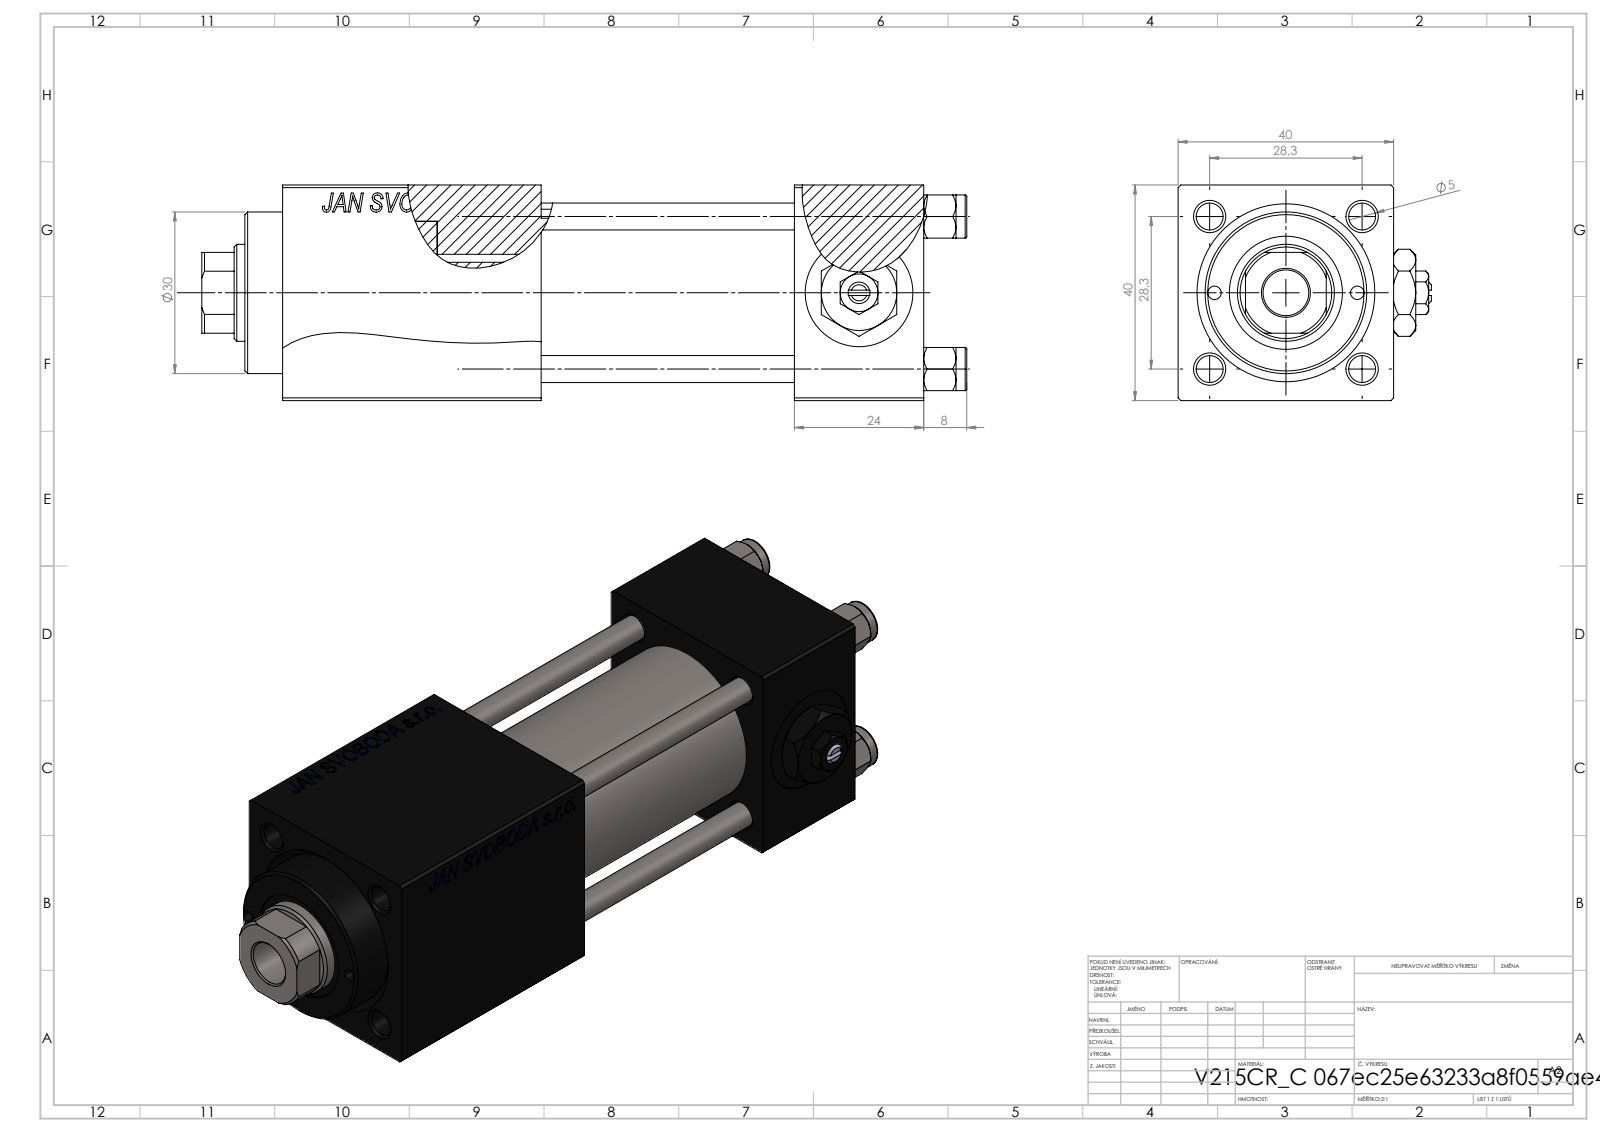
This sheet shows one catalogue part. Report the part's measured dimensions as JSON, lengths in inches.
{"part_name": "NUT_M5_C; V215CR_VCP_C; V215CR_C_TYCINKA; V215CR_C_Body (+2 more)", "step_written_by": "SolidWorks 2019 (CONFIG_CONTROL_DESIGN)", "units": "inches", "bodies": {"solids": 12, "faces": 1203, "planar": 549, "cylindrical": 96, "other": 558}, "overall_size": [5.591, 1.85, 1.575], "volume_in3": 9.1, "surface_area_in2": 89.79, "round_holes": [[0.197, 4], [0.787, 3], [0.098, 2], [0.276, 2], [0.518, 2], [0.335, 1], [0.709, 1], [0.827, 1], [0.984, 1], [1.181, 1]], "round_bosses_or_shafts": [[0.315, 4], [1.22, 1]], "partial_cylinders_radius": [[0.335, 1]], "face_to_face_distances": [1.575, 0.945, 1.85, 2.795, 3.555, 2.61, 0.76, 1.89, 1.567, 3.74], "hole_center_spacings": [0.558, 0.788, 1.114, 1.214, 0.522, 1.576, 1.043, 2.835]}
